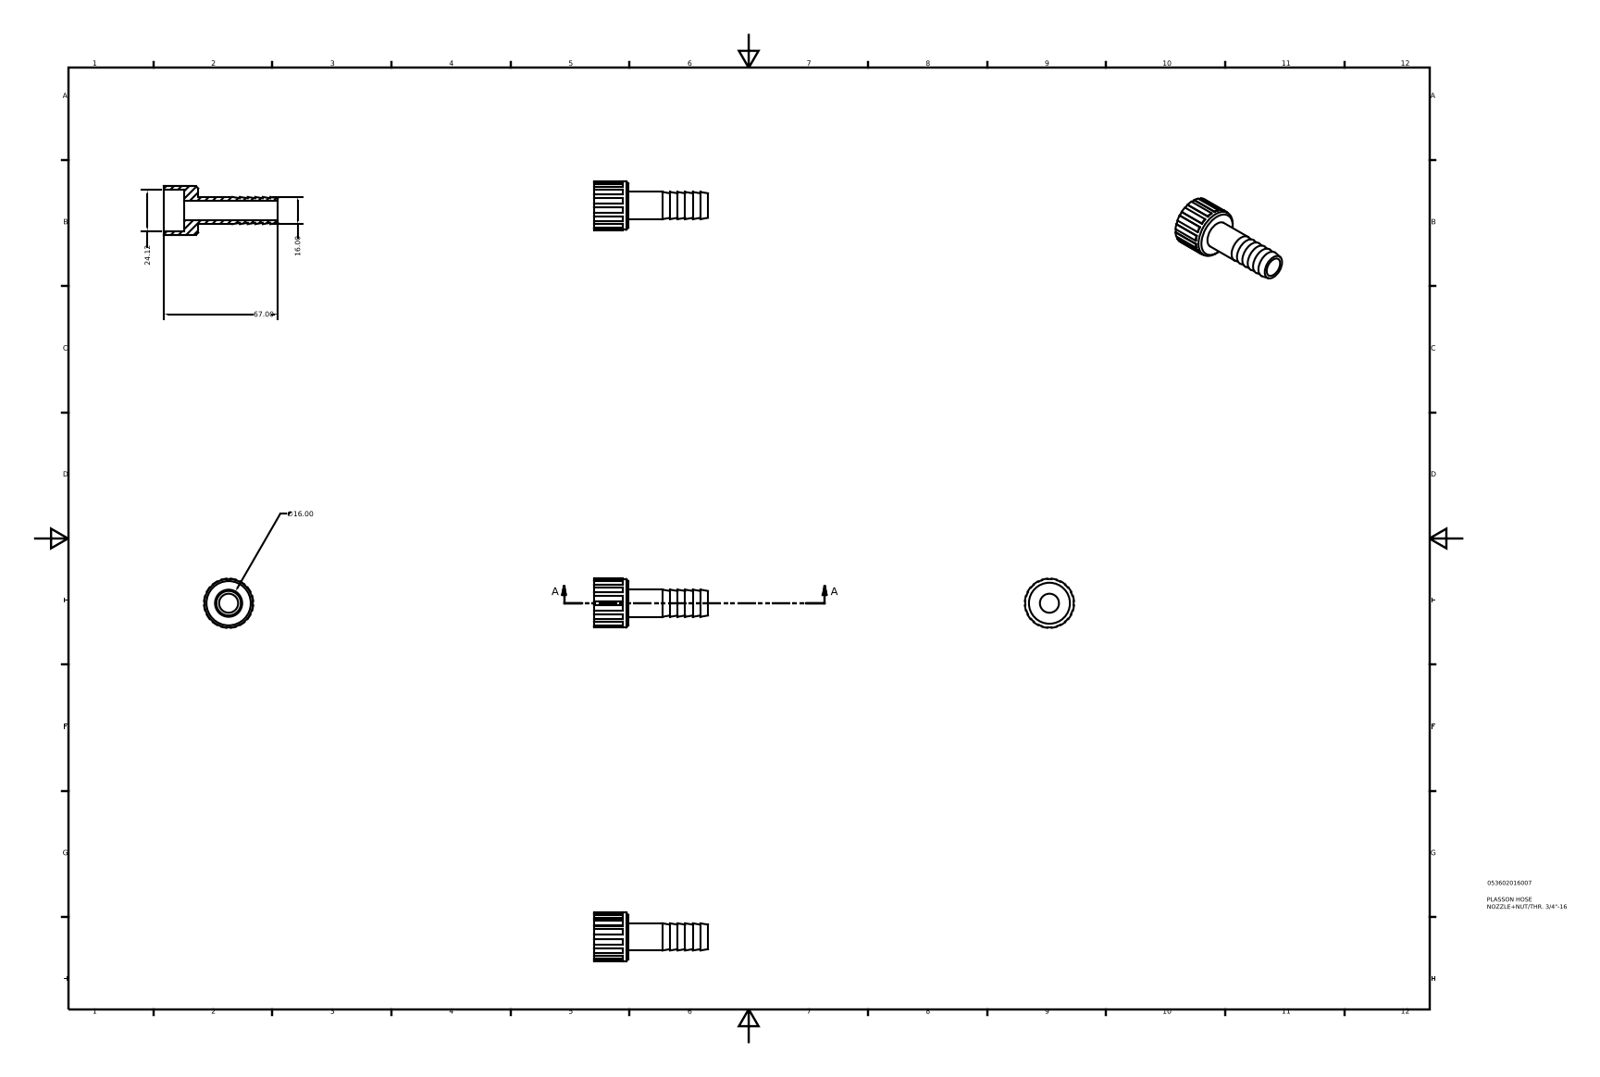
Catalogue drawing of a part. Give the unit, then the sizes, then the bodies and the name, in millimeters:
Units: millimetres
Overall size (bounding box): 67 × 28.84 × 28.84
Round holes (diameter × count): ⌀11.2 ×1, ⌀24.12 ×1
Round bosses / shafts (diameter × count): ⌀28.46 ×1, ⌀16 ×1
Partial cylindrical surfaces — rounded edges, fillets, slot ends (radius × count): R14.47 ×1
Main face-to-face distances: 8.04, 12.06, 20.1, 8.93, 13.4, 4.47, 4.46, 67, 54.94, 46.9
Volume: 10 926 mm³ · Surface area: 8 284 mm²
Bodies: 1 solid, 84 faces (57 planar, 20 cylindrical, 7 other)
Part name (STEP PRODUCT): 053602016007
STEP written by: Autodesk Inventor 2015 (AUTOMOTIVE_DESIGN)
